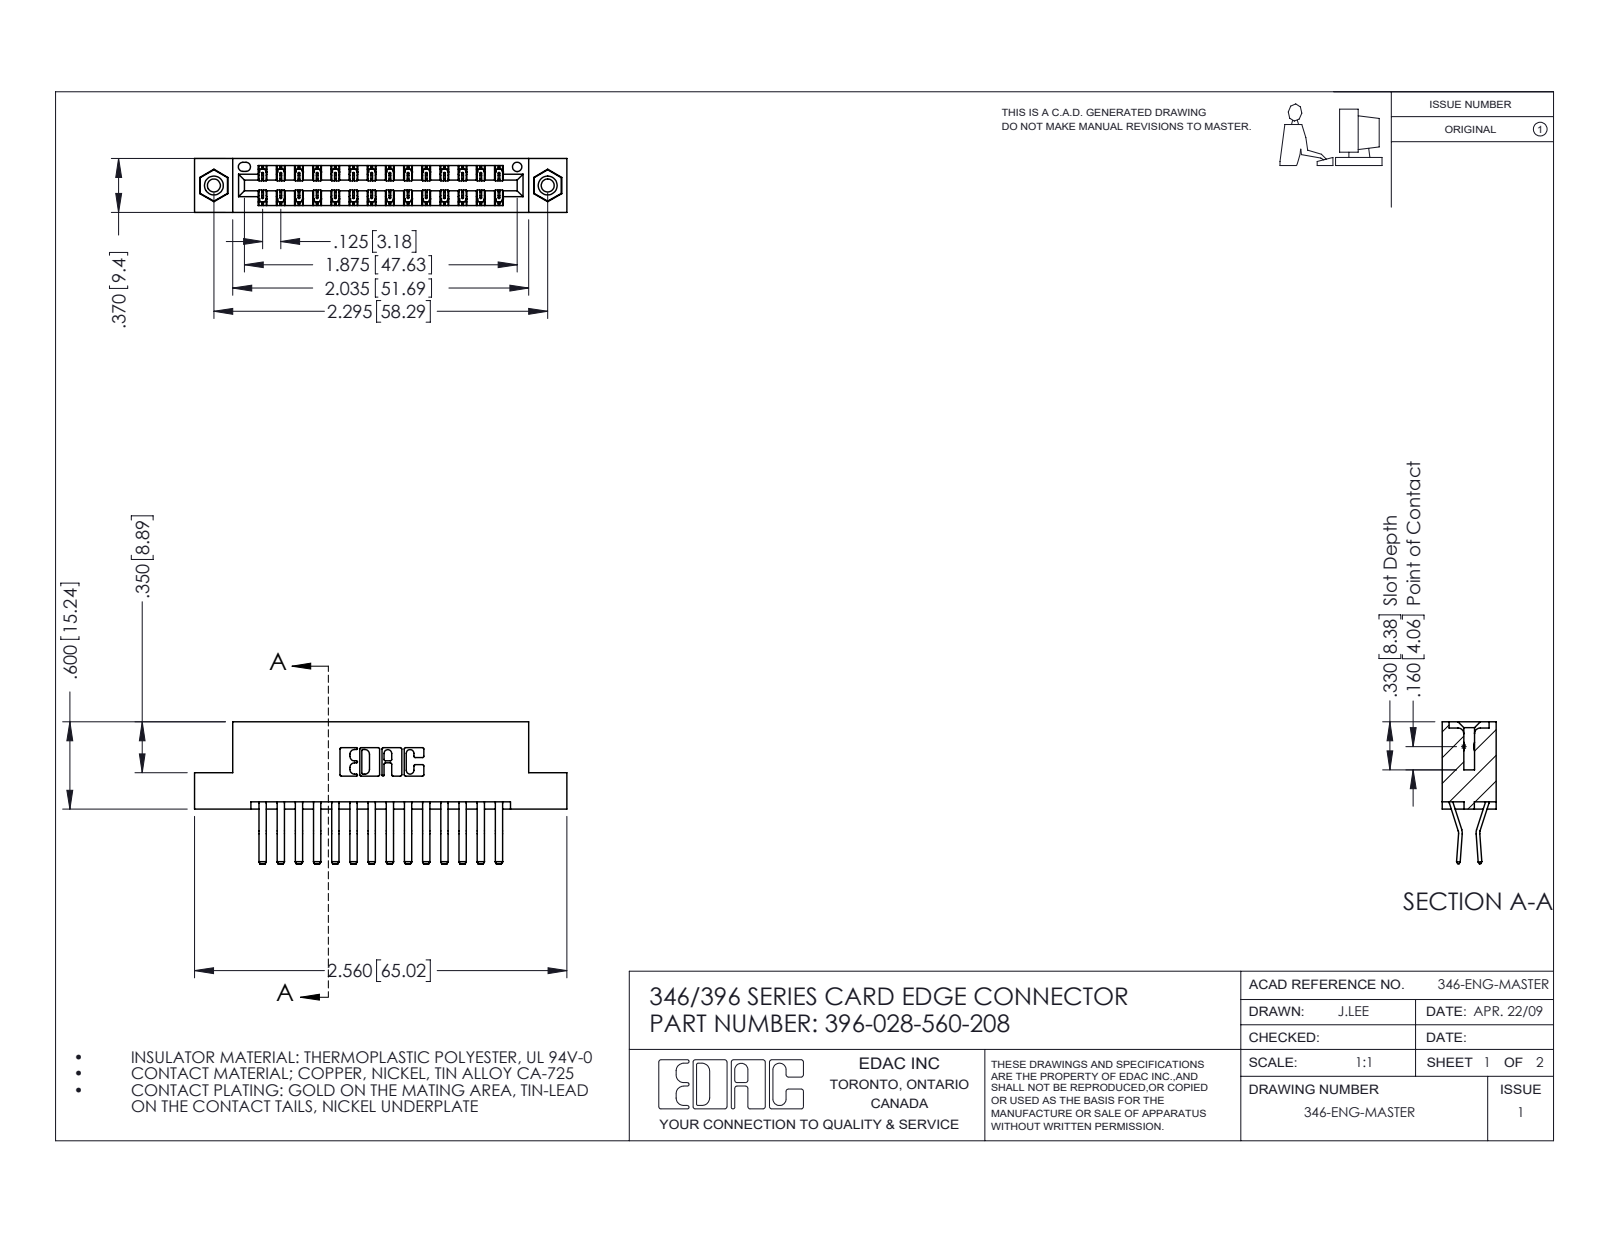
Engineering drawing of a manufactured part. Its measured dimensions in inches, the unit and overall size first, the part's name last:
Units: inches
Overall size (bounding box): 2.56 × 0.975 × 0.37
Round holes (diameter × count): ⌀0.089 ×2, ⌀0.125 ×2, ⌀0.156 ×2, ⌀0.064 ×1
Round bosses / shafts (diameter × count): ⌀0.155 ×2
Partial cylindrical surfaces — rounded edges, fillets, slot ends (radius × count): R0.006 ×42, R0.01 ×22, R0.007 ×6, R0.031 ×6, R0.026 ×3, R0.01 ×2, R0.014 ×2, R0.022 ×2
Main face-to-face distances: 0.048, 0.322, 0.25, 0.37, 0.025, 0.072, 0.298, 0.275, 0.148, 0.222
Hole centre spacings: 0.246, 2.089, 2.295
Volume: 0.384 in³ · Surface area: 13.53 in²
Bodies: 31 solids, 1694 faces (1088 planar, 590 cylindrical, 16 other)
Part name (STEP PRODUCT): 346 Part_Flush Mounting Lugs - 0.156 Dia-TI; 396-028-560-208; 345-250-001_345-250-003-102; 345-292-001_560 Tail
STEP written by: SolidWorks 2016 (CONFIG_CONTROL_DESIGN)
